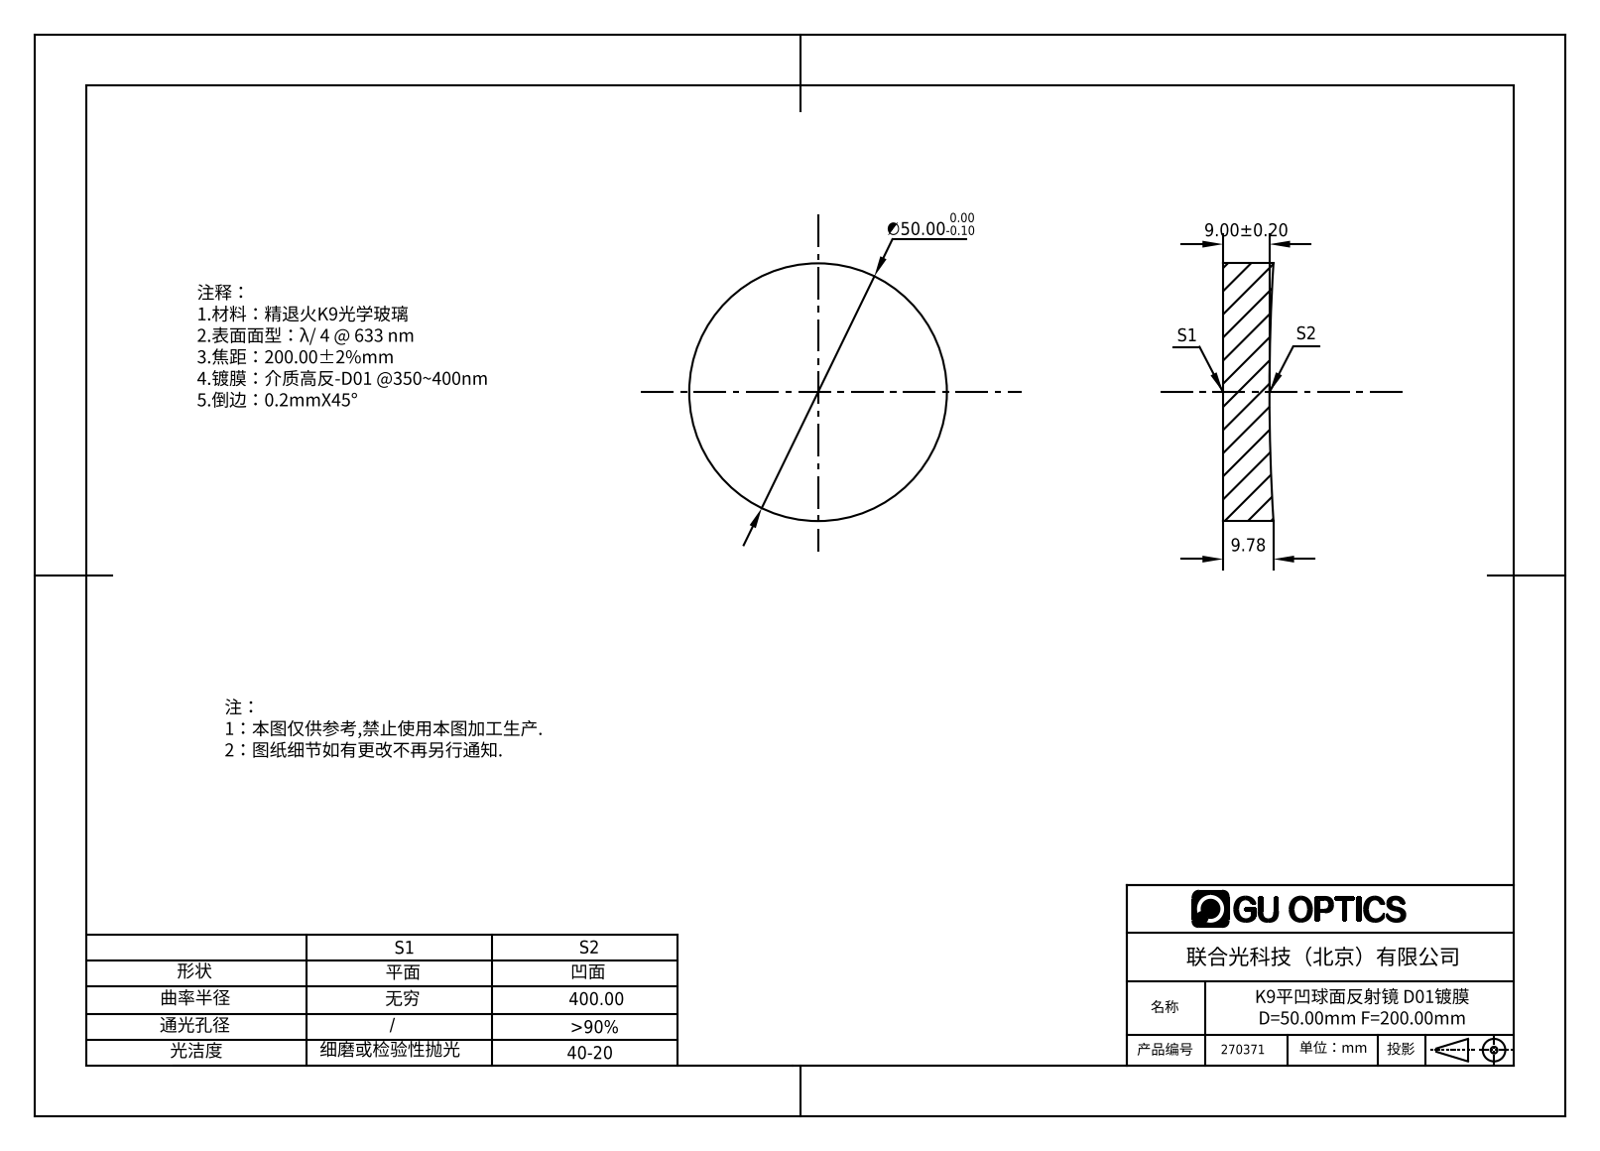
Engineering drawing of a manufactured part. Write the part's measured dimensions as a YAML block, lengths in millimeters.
part_name: "270046"
step_written_by: "SolidWorks 2016 (AUTOMOTIVE_DESIGN)"
units: millimeters
bodies: {solids: 1, faces: 5, planar: 1, cylindrical: 2, other: 2}
overall_size: [50, 50, 9.78]
volume: 18439
surface_area: 5465
round_bosses_or_shafts:
  - {diameter: 50, count: 1}
